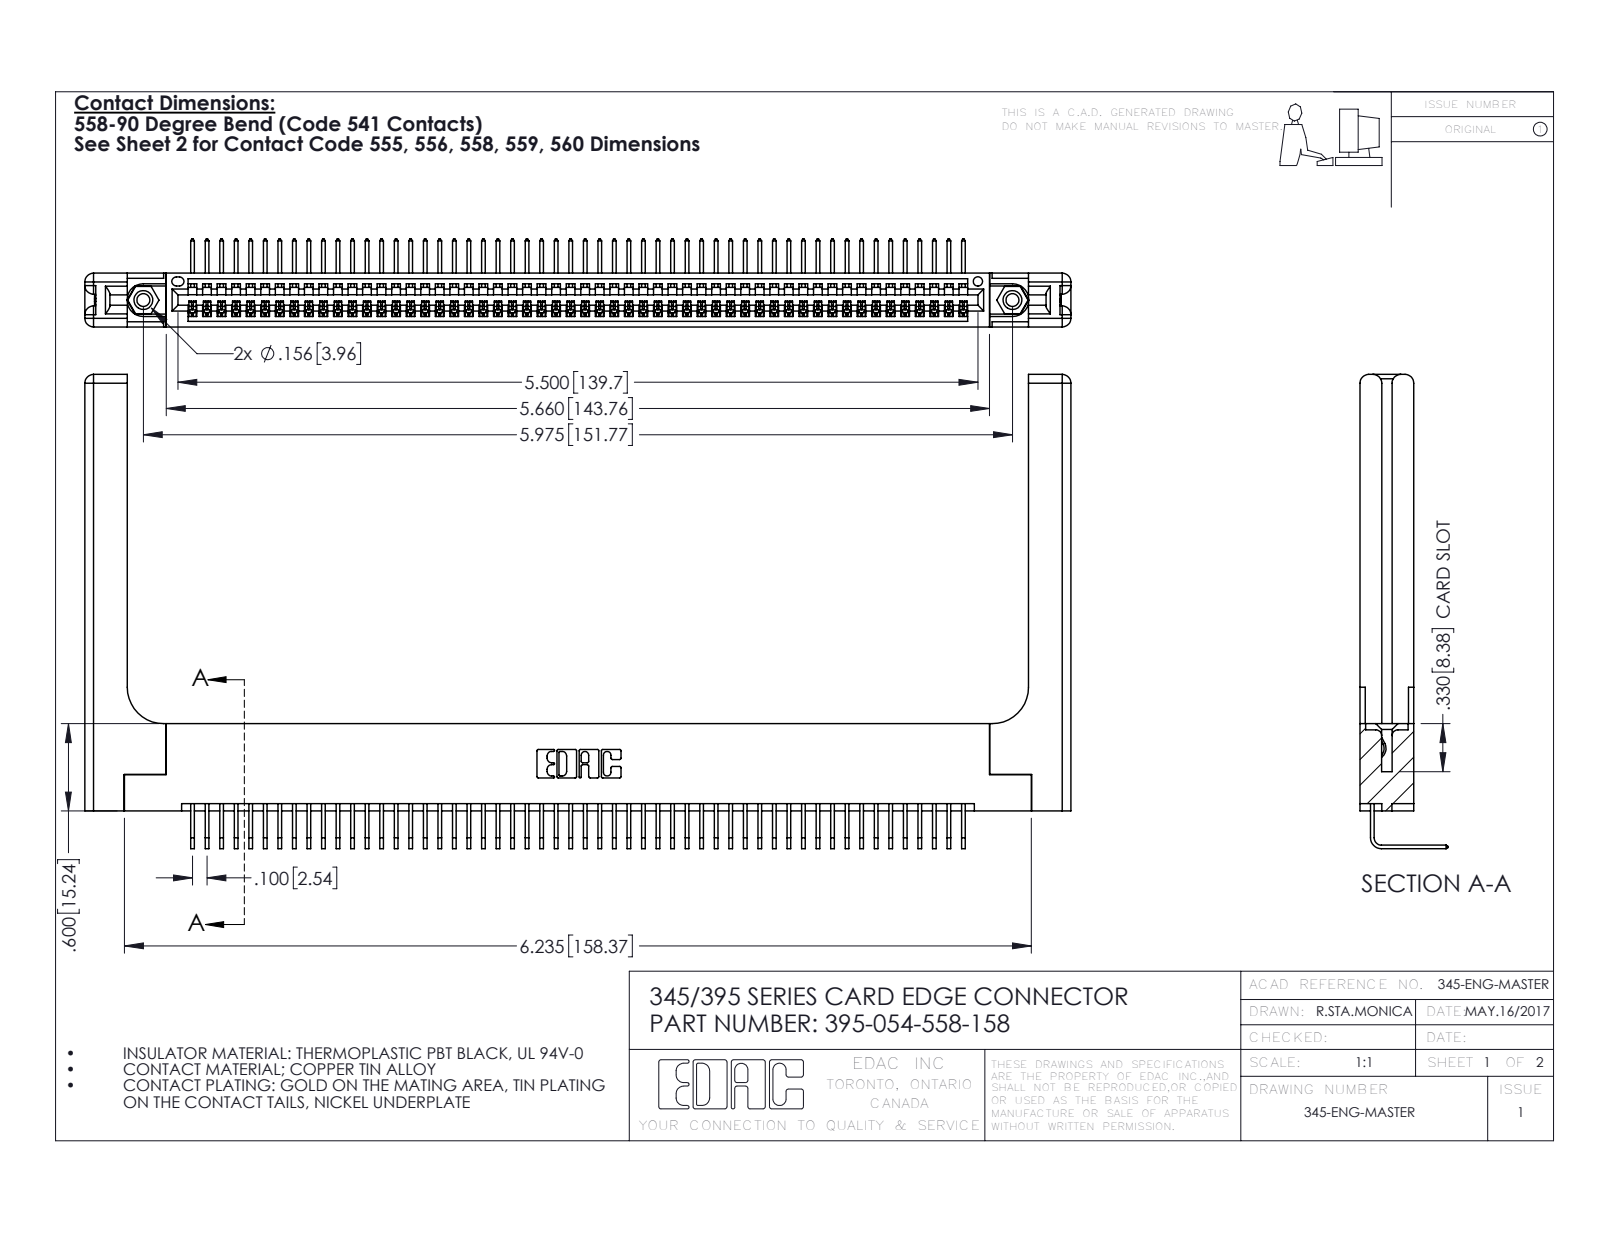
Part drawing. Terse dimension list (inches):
name: 395-054-558-158; 345-220-058_345-220-058; 345 Part_Flush Mounting Lugs - 0.156 Dia-TH; 345-250-001_345-250-001-102 (+1 more)
written by: SolidWorks 2016 (CONFIG_CONTROL_DESIGN)
unit: in
bodies: 59 solids, 3622 faces (2496 planar, 1066 cylindrical, 60 other)
size: 6.779 × 3.259 × 0.605
volume: 1.534 in³; area: 44.38 in²
holes: 2× ⌀0.089, 2× ⌀0.125, 2× ⌀0.156, 1× ⌀0.064
bosses: 2× ⌀0.155
rounds: 108× R0.006, 22× R0.01, 16× R0.06, 6× R0.007, 6× R0.031, 3× R0.026, 2× R0.03, 2× R0.031
face distances: 0.072, 0.37, 0.298, 0.2, 0.098, 0.272, 0.025, 0.225, 0.148, 0.15
hole spacings: 0.27, 5.739, 5.975
